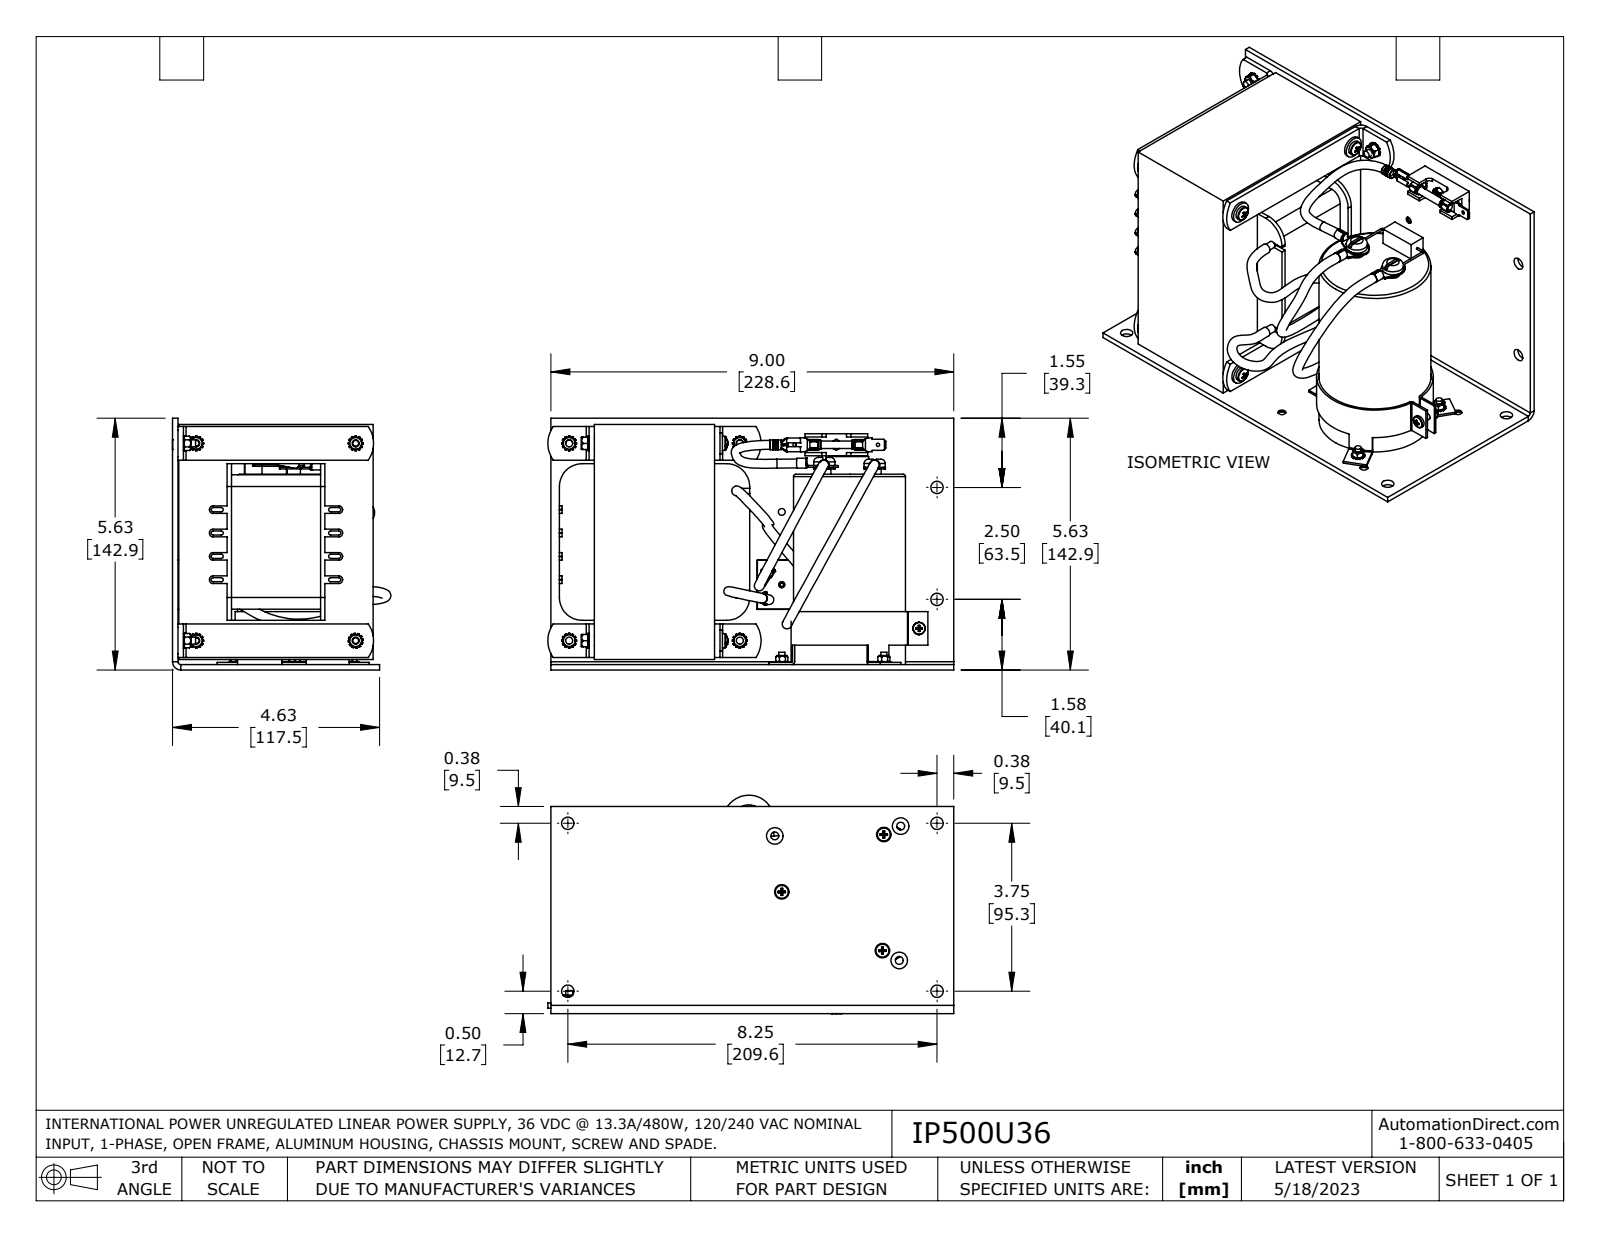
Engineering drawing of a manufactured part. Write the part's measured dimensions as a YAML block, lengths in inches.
part_name: "IP500U36"
step_written_by: "SolidWorks 2021 (AUTOMOTIVE_DESIGN)"
units: inches
bodies: {solids: 71, faces: 2232, planar: 1176, cylindrical: 735, other: 321}
overall_size: [9.07, 5.625, 4.88]
volume: 101.9
surface_area: 484.6
round_holes:
  - {diameter: 0.157, count: 9}
  - {diameter: 0.177, count: 9}
  - {diameter: 0.13, count: 8}
  - {diameter: 0.169, count: 8}
  - {diameter: 0.276, count: 8}
  - {diameter: 0.138, count: 6}
  - {diameter: 0.154, count: 5}
  - {diameter: 0.181, count: 5}
  - {diameter: 0.114, count: 4}
  - {diameter: 0.15, count: 4}
  - {diameter: 0.192, count: 4}
  - {diameter: 0.126, count: 3}
round_bosses_or_shafts:
  - {diameter: 0.472, count: 6}
  - {diameter: 0.039, count: 6}
  - {diameter: 0.217, count: 5}
  - {diameter: 0.21, count: 5}
  - {diameter: 0.331, count: 4}
  - {diameter: 0.315, count: 4}
  - {diameter: 0.287, count: 4}
  - {diameter: 0.224, count: 3}
partial_cylinders:
  - {radius: 0.014, count: 20}
  - {radius: 0.046, count: 16}
  - {radius: 0.08, count: 16}
  - {radius: 0.024, count: 12}
  - {radius: 0.021, count: 10}
  - {radius: 0.037, count: 10}
  - {radius: 0.055, count: 10}
  - {radius: 0.126, count: 8}
face_to_face_distances: [0.122, 2.687, 4.359, 0.118, 0.016, 0.138, 4.481, 4.344, 2.806, 0.25]
hole_center_spacings: [3.813, 4.406, 8.25, 0.931, 1.226, 1.51, 2.157, 2.5]
